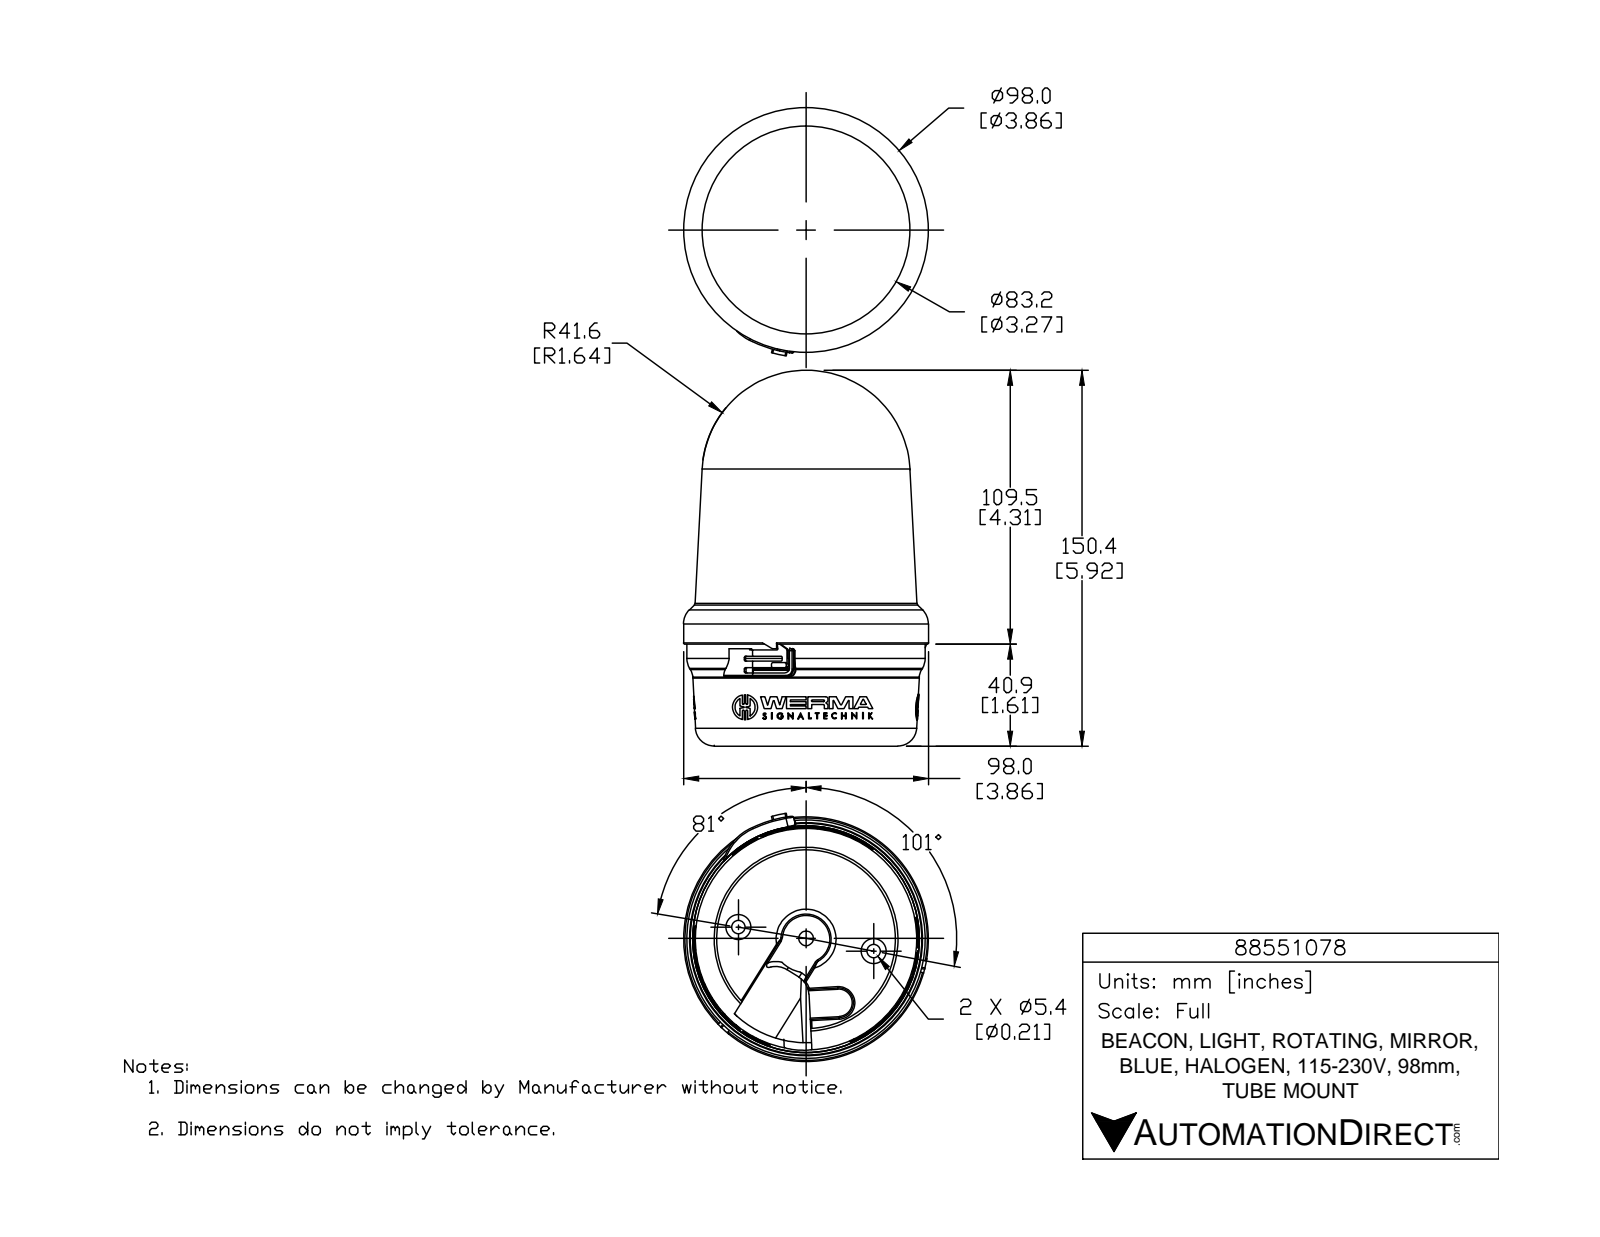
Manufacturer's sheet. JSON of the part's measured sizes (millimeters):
{"part_name": "88551078", "step_written_by": "SolidWorks 2015 (AUTOMOTIVE_DESIGN)", "units": "millimeters", "bodies": {"solids": 1, "faces": 1006, "planar": 554, "cylindrical": 189, "other": 263}, "overall_size": [201, 99.4, 98], "volume_mm3": 896400, "surface_area_mm2": 58960, "round_holes": [[2, 3], [25.7, 1], [26, 1]], "round_bosses_or_shafts": [[11.5, 3], [2.9, 3], [98, 1], [35.8, 1], [32, 1]], "partial_cylinders_radius": [[0.5, 12], [0.2, 9], [0.2, 6], [0.4, 6], [0.4, 6], [0.4, 6], [6.7, 6], [0.2, 3]], "face_to_face_distances": [56.2, 11.7, 68, 8.5, 3.2, 64.7, 66.1, 62.9, 54.4, 1.9]}
